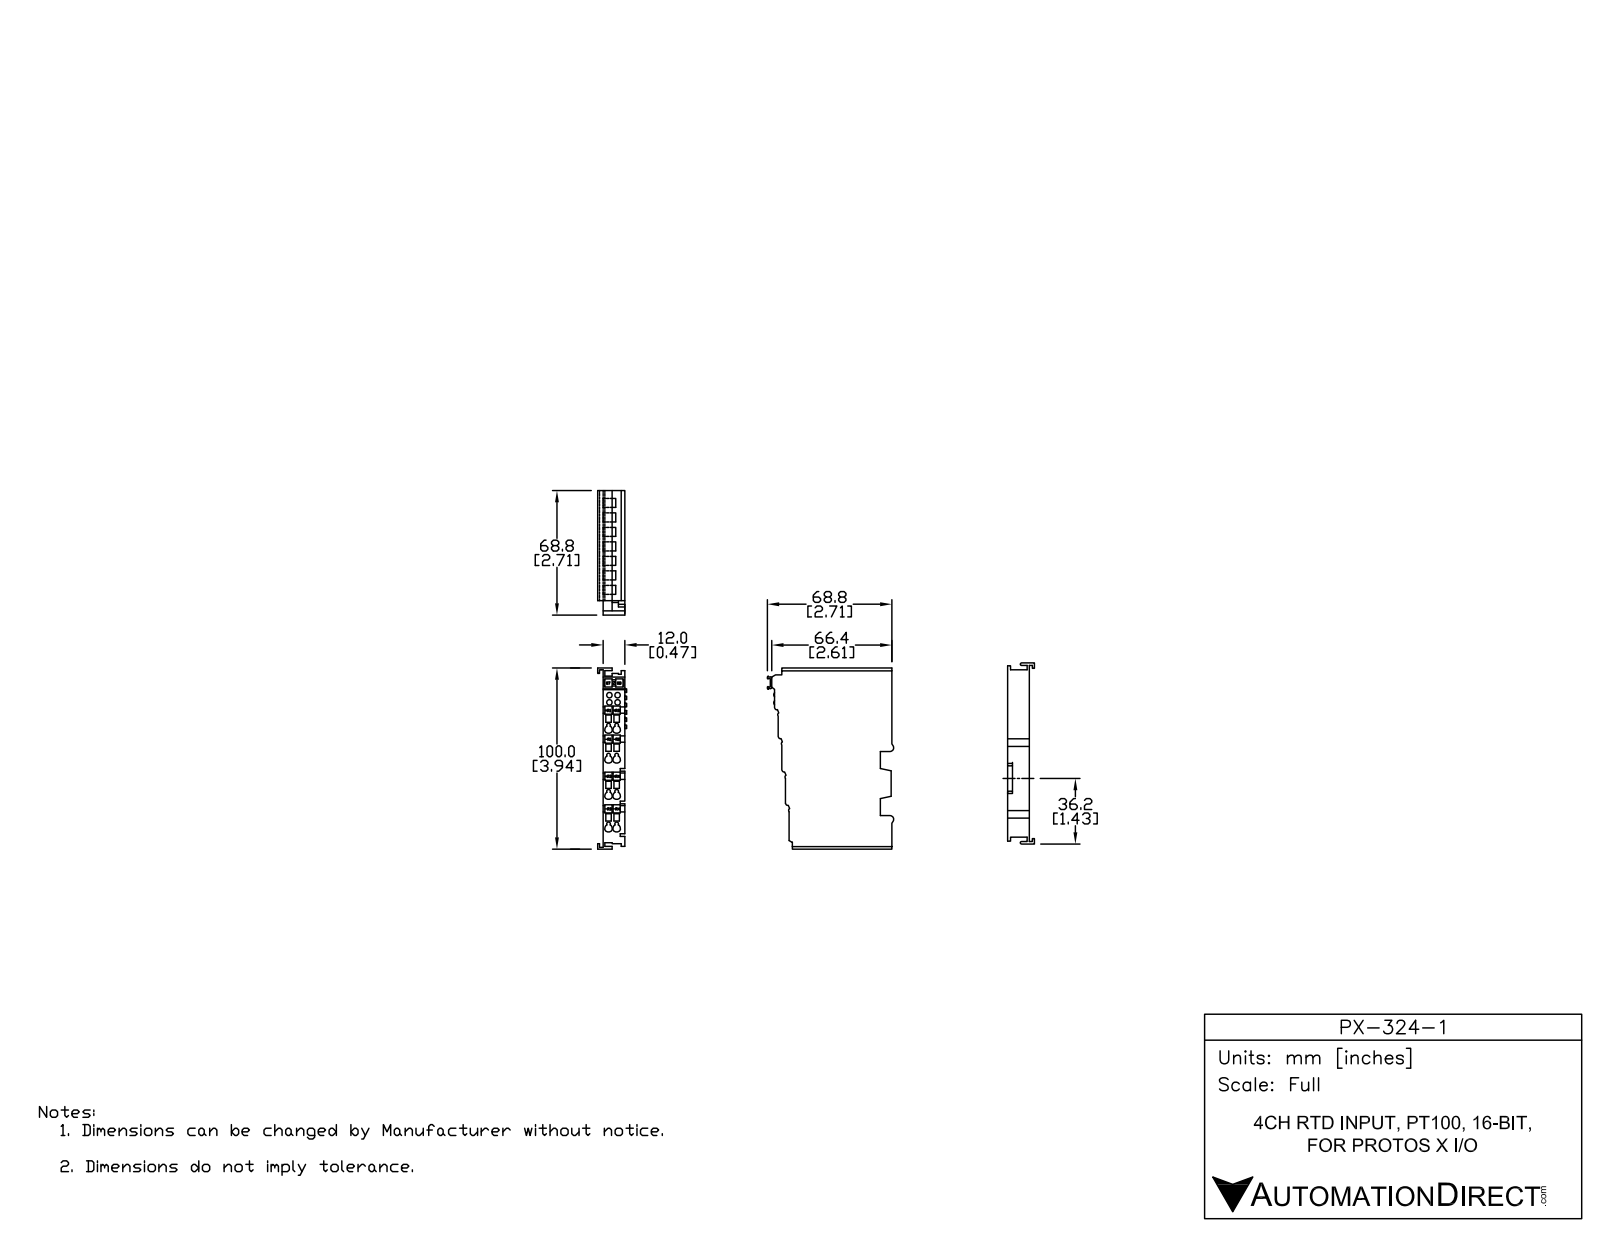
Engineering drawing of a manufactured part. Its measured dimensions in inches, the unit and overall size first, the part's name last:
Units: inches
Overall size (bounding box): 3.947 × 2.806 × 0.596
Round holes (diameter × count): ⌀0.157 ×8, ⌀0.138 ×4
Partial cylindrical surfaces — rounded edges, fillets, slot ends (radius × count): R0.012 ×46, R0.01 ×35, R0.015 ×12, R0.005 ×10, R0.039 ×9, R0.016 ×8, R0.007 ×4, R0.041 ×4
Main face-to-face distances: 0.472, 0.039, 0.079, 0.394, 0.073, 0.433, 0.343, 0.157, 0.124, 0.048
Hole centre spacings: 0.177, 0.197, 0.724, 0.751, 0.25, 0.63, 0.66, 0.804
Volume: 3.564 in³ · Surface area: 52.52 in²
Bodies: 28 solids, 1367 faces (963 planar, 344 cylindrical, 60 other)
Part name (STEP PRODUCT): PX-324
STEP written by: SolidWorks 2014 (AUTOMOTIVE_DESIGN)
